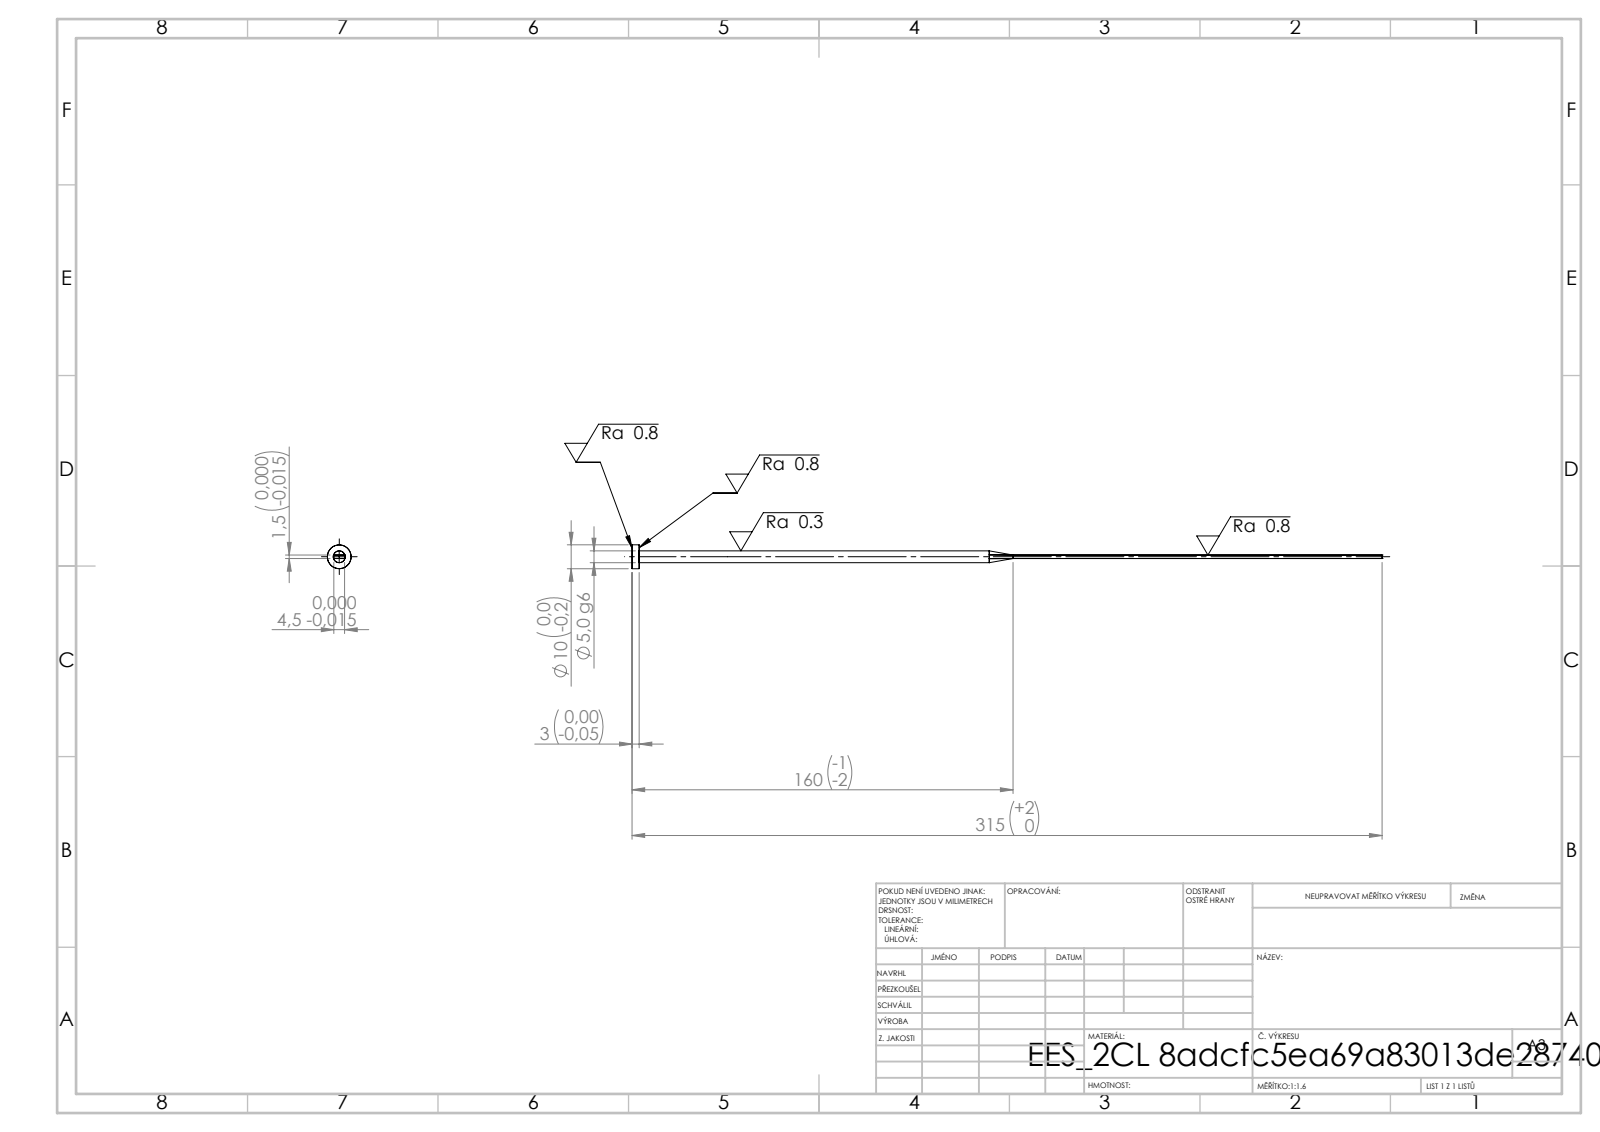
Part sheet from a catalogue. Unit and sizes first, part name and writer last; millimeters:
Units: millimetres
Overall size (bounding box): 315 × 10 × 10
Round bosses / shafts (diameter × count): ⌀10 ×1, ⌀5 ×1
Main face-to-face distances: 1.5, 4.5, 3, 315, 312
Volume: 4 296 mm³ · Surface area: 4 542 mm²
Bodies: 1 solid, 15 faces (7 planar, 4 cylindrical, 4 other)
STEP written by: SolidWorks 2019 (CONFIG_CONTROL_DESIGN)
